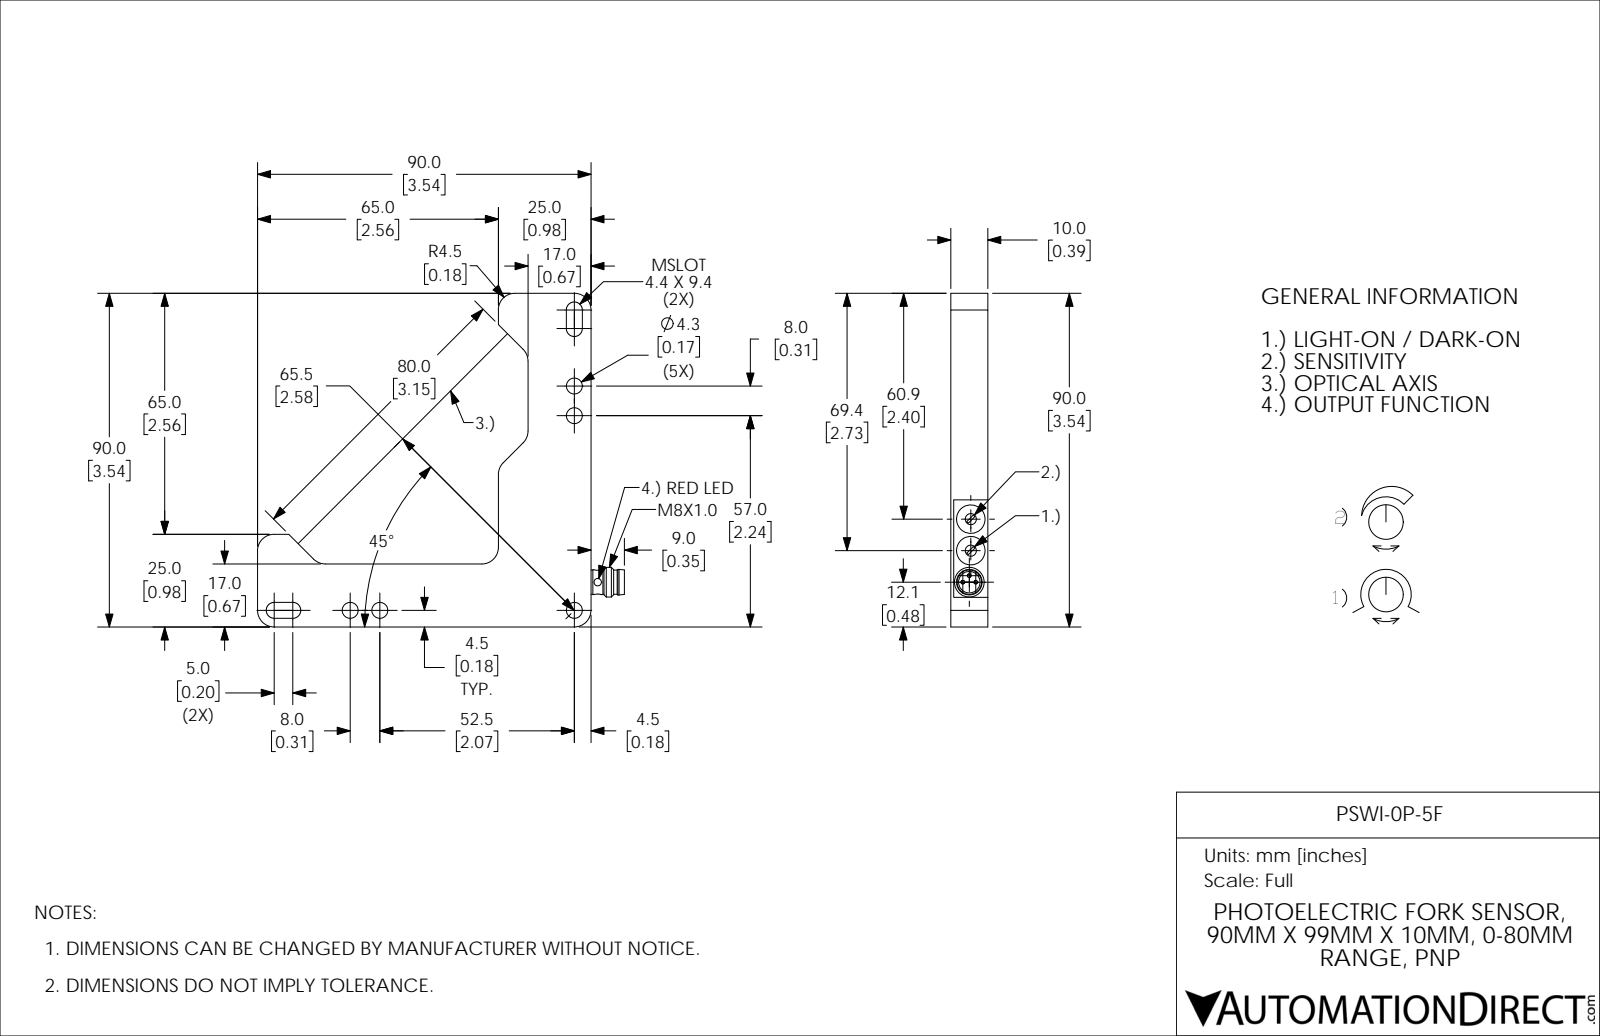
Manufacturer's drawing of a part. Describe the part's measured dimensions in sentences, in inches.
The part is named "PSWI-0P-5F". Its 3-D file was written by "SolidWorks 2017 (AUTOMOTIVE_DESIGN)". It is 1 solid with 90 faces: 42 planar, 41 cylindrical and 7 other. Overall it measures 3.898 by 3.543 by 0.394 inches. Its volume is 1.872 cubic inches and its surface area 17.48 square inches. Round holes: 5 of diameter 0.169, 2 of diameter 0.079, 2 of diameter 0.118, 2 of diameter 0.303, 1 of diameter 0.228. Round bosses or shafts: 3 of diameter 0.039, 1 of diameter 0.315, 1 of diameter 0.272, 1 of diameter 0.264, 1 of diameter 0.257. Partial cylindrical surfaces (rounded edges, fillets, slot ends): 10 of radius 0.177, 4 of radius 0.085, 2 of radius 0.049. The main face-to-face distances are 0.394, 0.669, 3.543, 2.874, 0.984, 0.315, 2.559, 3.539, 0.98, 0.665. The hole center spacings are 0.315, 2.067, 2.382, 3.154, 0.335, 0.335, 0.389, 0.669.
